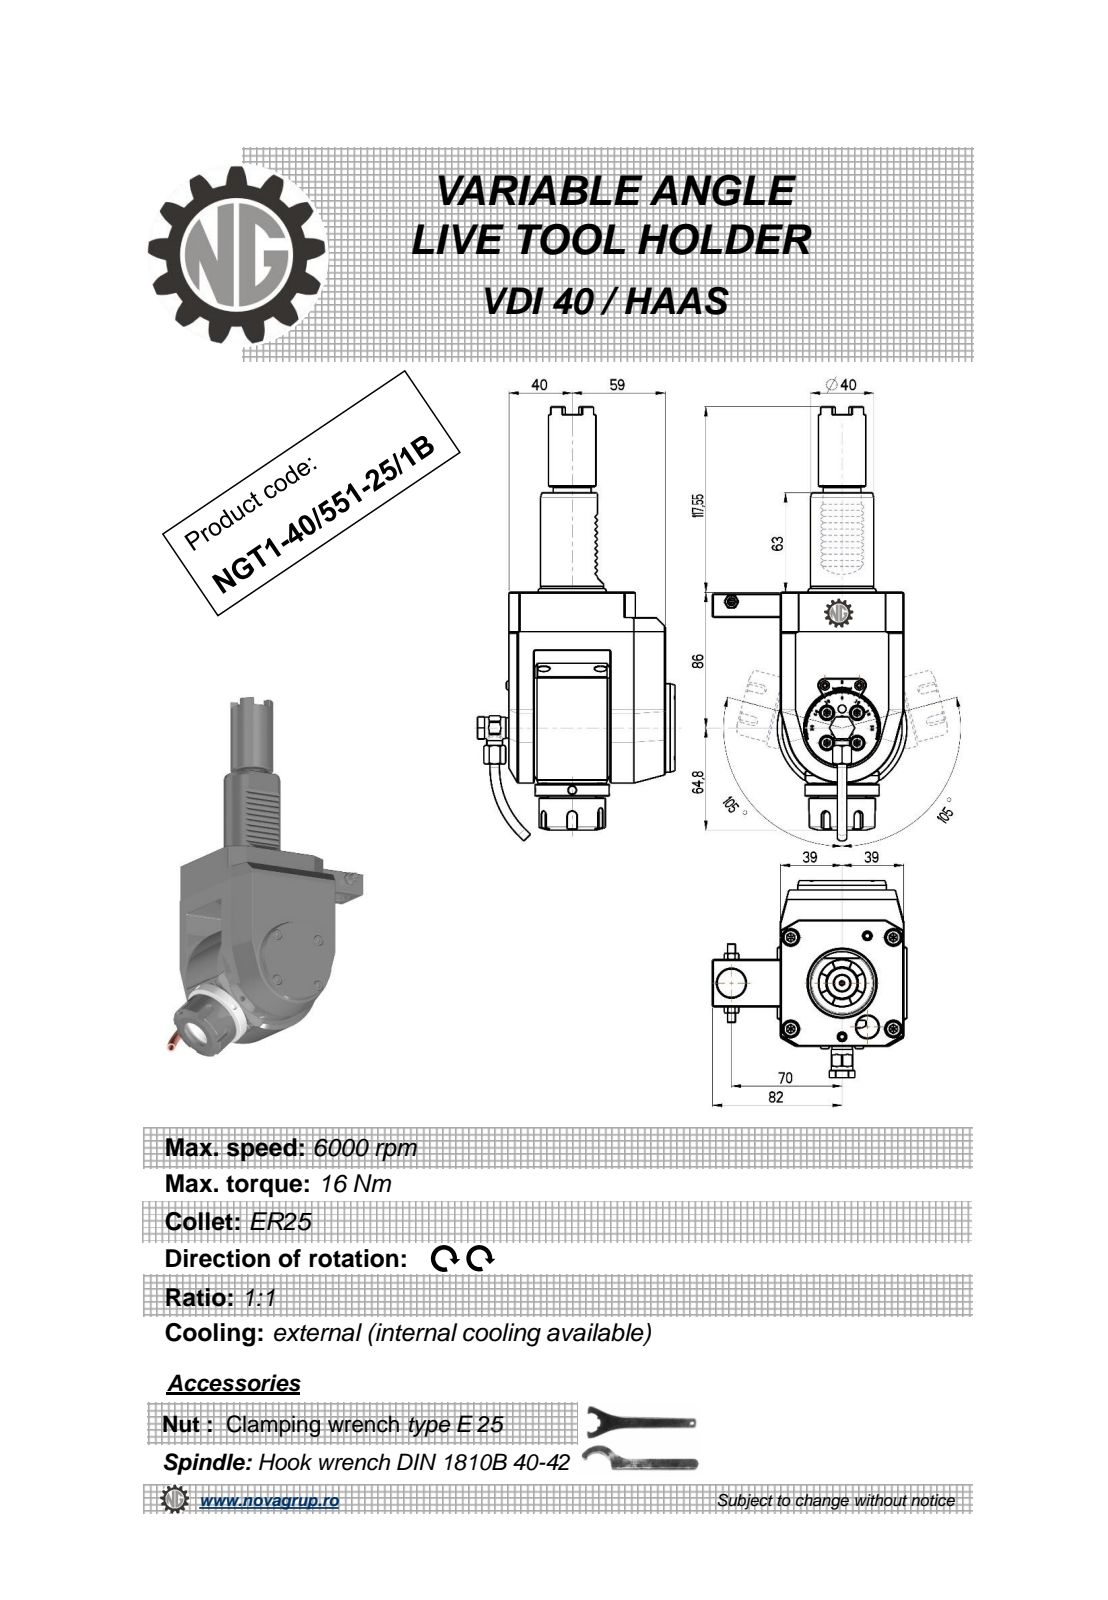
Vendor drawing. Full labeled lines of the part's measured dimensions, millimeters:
Part name (STEP PRODUCT): NGT1_40_551_25_1B
STEP written by: PRO/ENGINEER BY PARAMETRIC TECHNOLOGY CORPORATION, 2010280 (CONFIG_CONTROL_DESIGN)
Units: millimetres
Bodies: 1 solid, 601 faces (266 planar, 140 cylindrical, 195 other)
Overall size (bounding box): 275.22 × 124.9 × 123
Volume: 959 162 mm³ · Surface area: 90 588 mm²
Round holes (diameter × count): ⌀4 ×3, ⌀5 ×2, ⌀3 ×1, ⌀4.2 ×1, ⌀6.2 ×1, ⌀9 ×1, ⌀9.5 ×1, ⌀11 ×1, ⌀18 ×1, ⌀20.3 ×1
Round bosses / shafts (diameter × count): ⌀10 ×2, ⌀6 ×2, ⌀5.7 ×2, ⌀82 ×1, ⌀56 ×1, ⌀47 ×1, ⌀42 ×1, ⌀40 ×1
Partial cylindrical surfaces — rounded edges, fillets, slot ends (radius × count): R0.26 ×12, R0.3 ×10, R3 ×5, R0.5 ×4, R10 ×3, R1 ×2, R7.7 ×1, R35 ×1
Main face-to-face distances: 16, 37, 64, 99, 78, 6, 105, 1, 21, 25
Hole centre spacings: 0.4, 39.45, 49, 49.4, 70, 85.45, 85.68, 106.3
